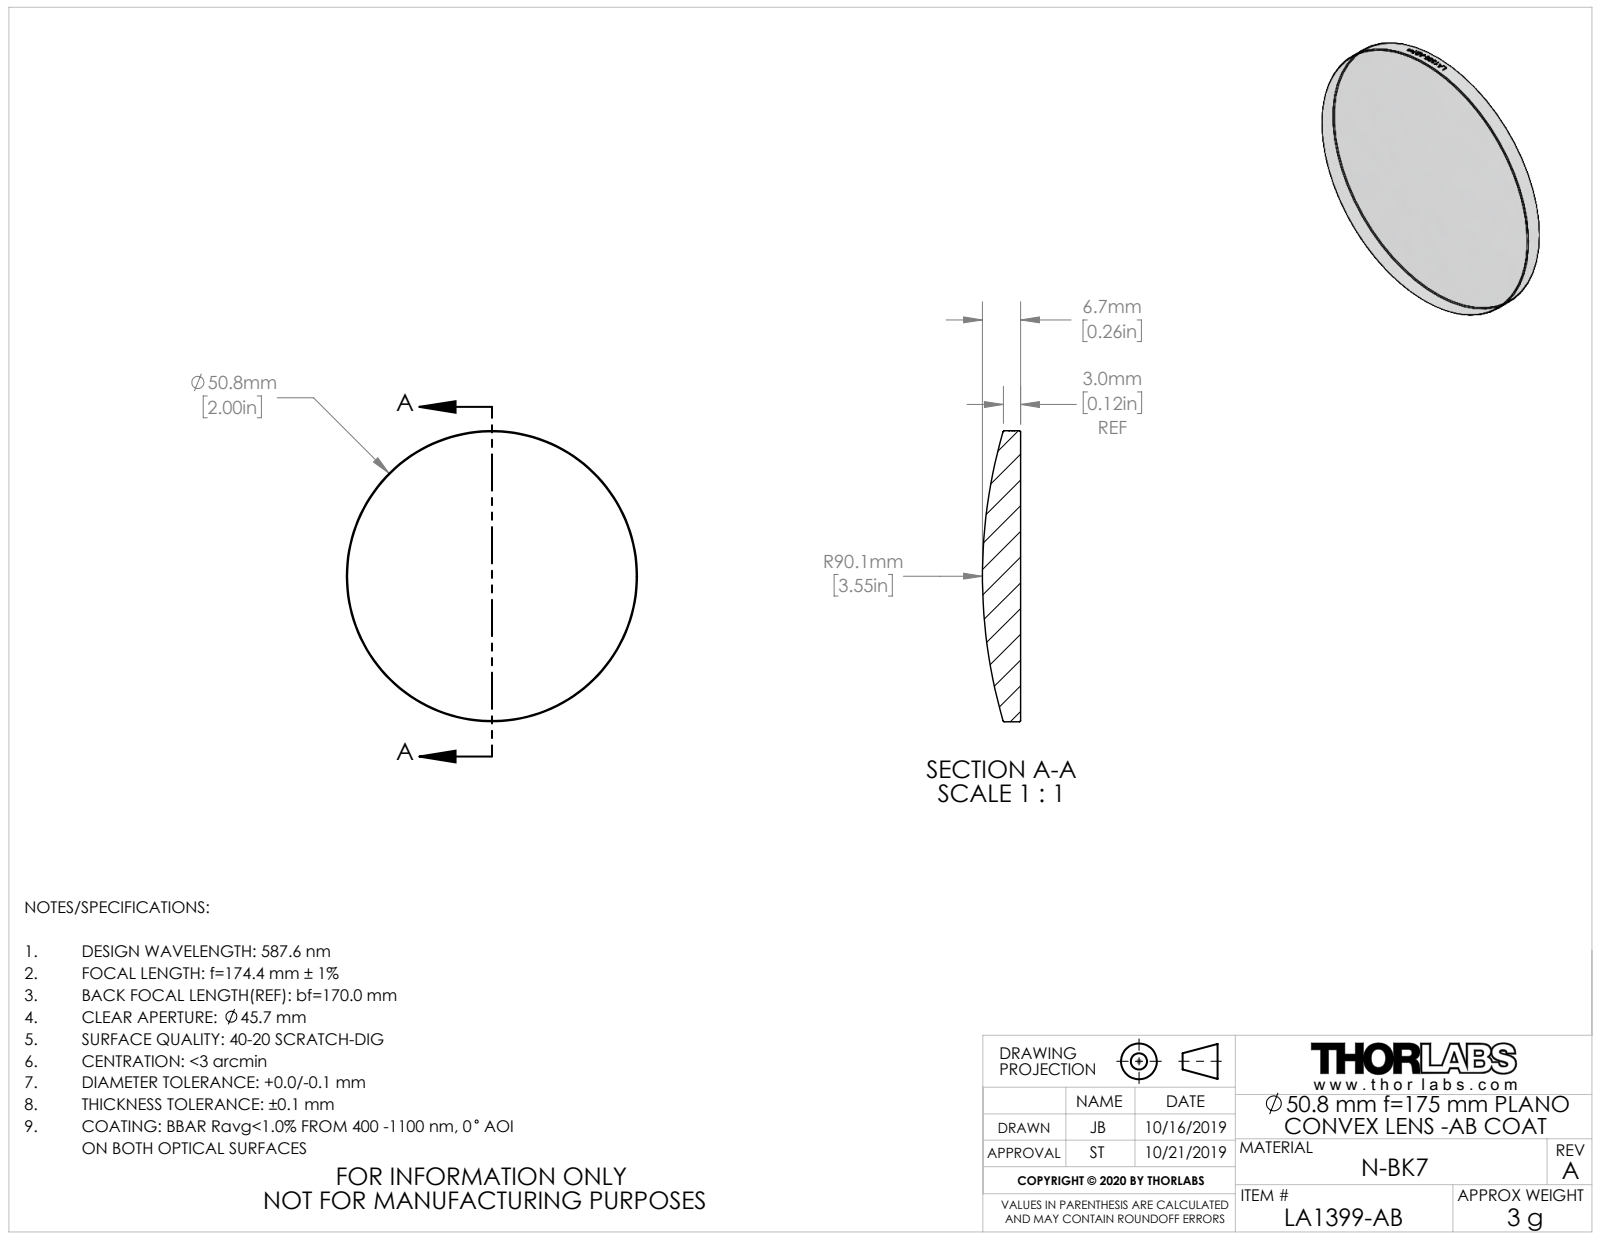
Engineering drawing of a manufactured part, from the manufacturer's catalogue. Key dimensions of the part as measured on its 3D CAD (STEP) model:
Part name (STEP PRODUCT): TTN195806-E0W
STEP written by: SolidWorks 2018 (CONFIG_CONTROL_DESIGN)
Units: millimetres
Bodies: 1 solid, 28 faces (1 planar, 21 cylindrical, 6 other)
Overall size (bounding box): 50.8 × 50.8 × 6.65
Volume: 9 798 mm³ · Surface area: 4 548 mm²
Round bosses / shafts (diameter × count): ⌀50.8 ×1
